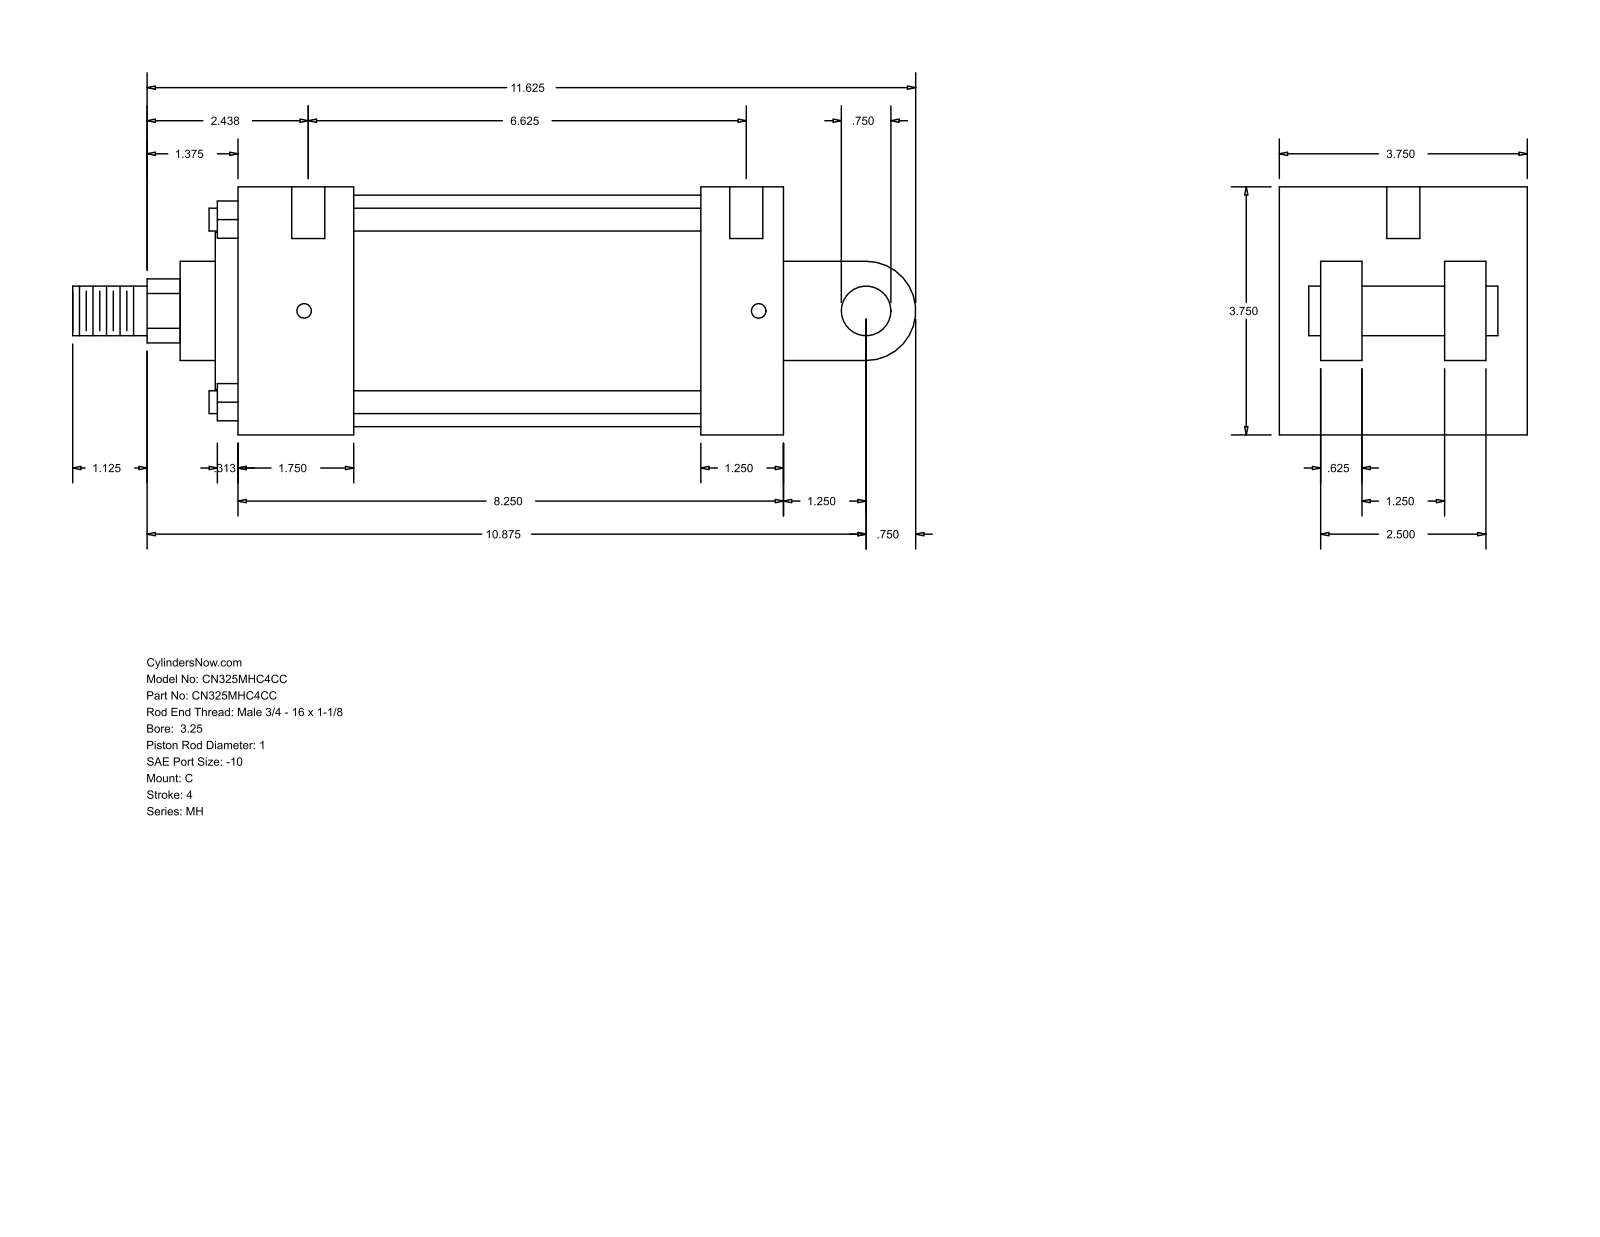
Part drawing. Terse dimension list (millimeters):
name: MH_C__0325_1
written by: GSSL Pune (CONFIG_CONTROL_DESIGN)
unit: mm
bodies: 0 solids, 101 faces (71 planar, 30 cylindrical, 0 other)
size: 323.85 × 95.25 × 95.25
holes: 4× ⌀5.56, 2× ⌀12.7
bosses: 4× ⌀8.76, 2× ⌀19.05, 1× ⌀88.9, 1× ⌀60.33, 1× ⌀38.1, 1× ⌀25.4
rounds: 1× R12.29, 1× R19.05
face distances: 95.24, 15.87, 209.55, 63.5, 79.37, 31.74, 47.63, 44.46, 177.8, 133.34
hole spacings: 174.62, 1.58, 4.76, 168.28, 169.86, 173.04
